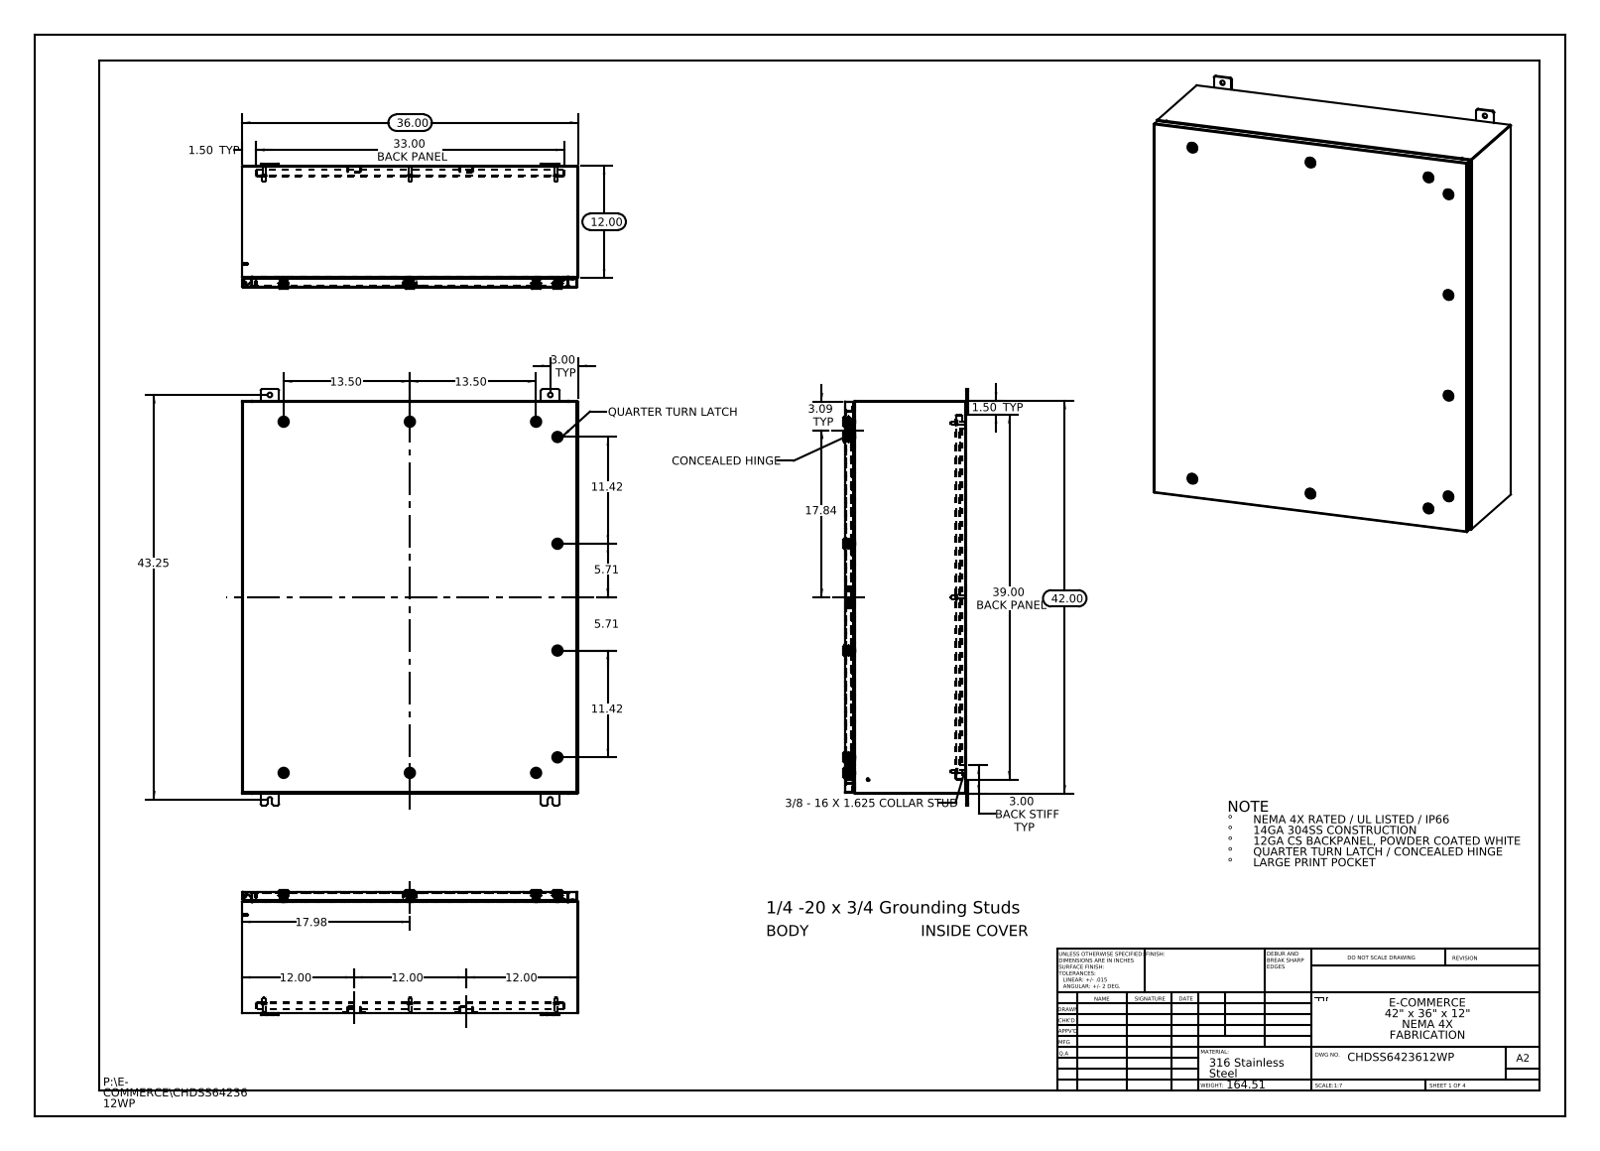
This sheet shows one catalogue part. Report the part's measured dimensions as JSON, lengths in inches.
{"part_name": "CHDSS6423612WP Mounting Studs; Housing-211301-IB-Industrilas_Housing-211301-IB-Industrilas; CHDSS6423612WP Enclosure Stiffener; CHDSS6423612WP Body (+8 more)", "step_written_by": "SolidWorks 2013 (CONFIG_CONTROL_DESIGN)", "units": "inches", "bodies": {"solids": 90, "faces": 8952, "planar": 2558, "cylindrical": 2786, "other": 3608}, "overall_size": [44.5, 36, 13.356], "volume_in3": 580.9, "surface_area_in2": 14456, "round_holes": [[0.5, 12], [0.197, 10], [0.394, 10], [0.4, 10], [0.63, 10], [0.787, 10], [0.25, 6], [0.136, 2], [0.211, 1]], "round_bosses_or_shafts": [[0.236, 12], [1.102, 10], [0.78, 10], [0.626, 10], [0.61, 10], [0.531, 10], [0.392, 10], [0.114, 10]], "partial_cylinders_radius": [[0.006, 330], [0.118, 330], [0.028, 120], [0.02, 40], [0.197, 40], [0.013, 34], [0.088, 30], [0.19, 24]], "face_to_face_distances": [0.075, 0.074, 12.861, 12.936, 13.01, 12.935, 0.104, 1, 1.075, 11.861], "hole_center_spacings": [13.5, 17, 17.145, 18.625, 24.311, 36.379, 39.903, 40.394]}
